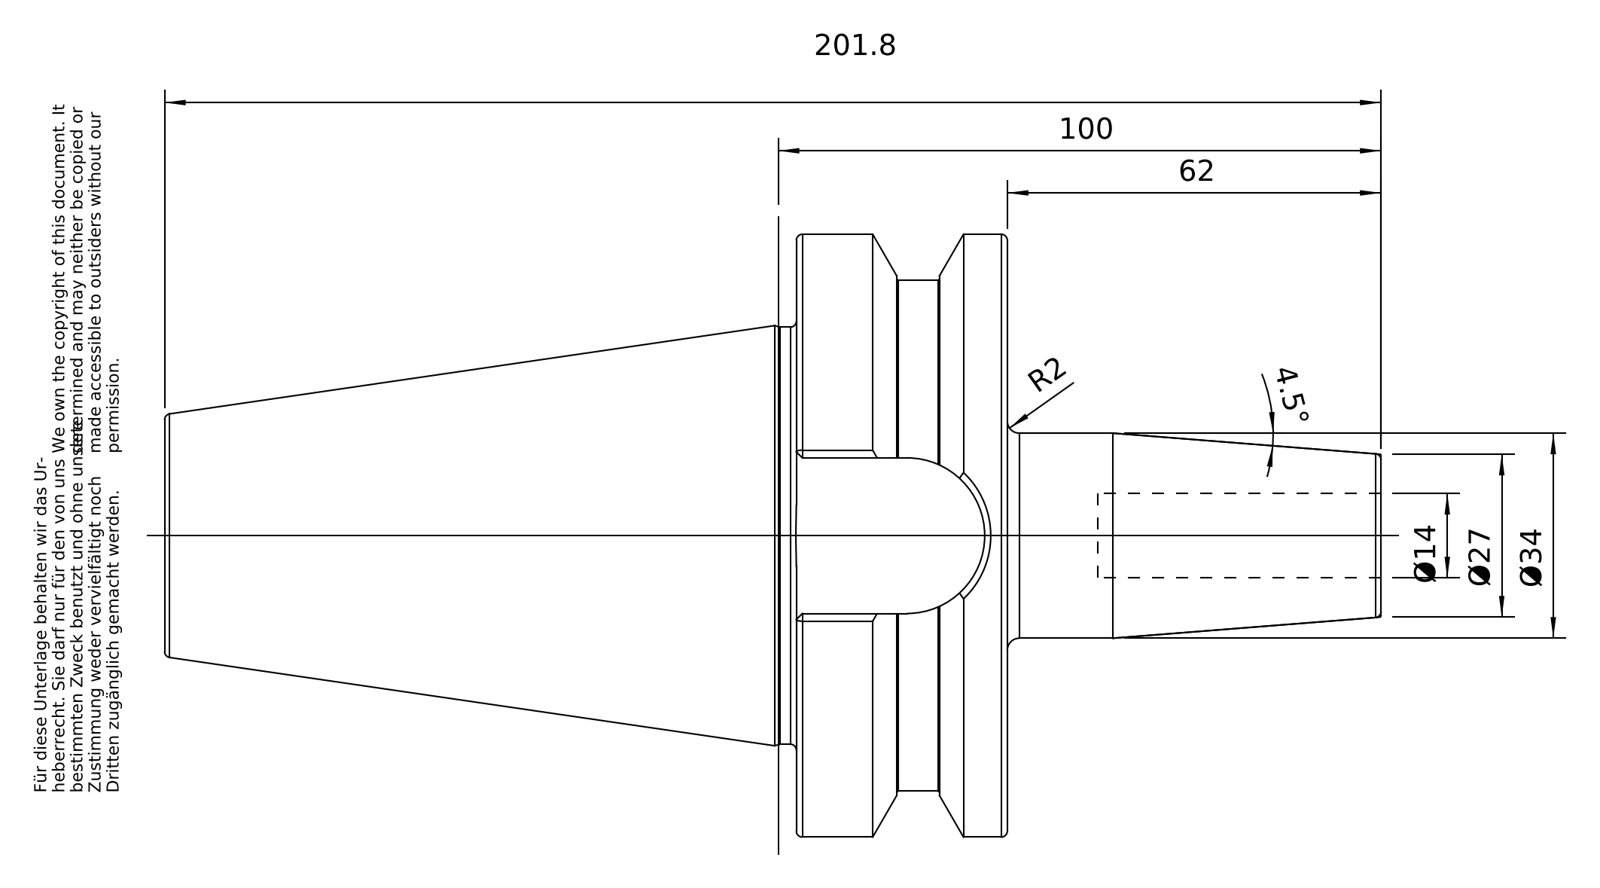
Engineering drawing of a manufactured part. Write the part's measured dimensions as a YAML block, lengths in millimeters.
part_name: "50-640-14"
step_written_by: "PRO/ENGINEER BY PARAMETRIC TECHNOLOGY CORPORATION, 2010430 (CONFIG_CONTROL_DESIGN)"
units: millimeters
bodies: {solids: 1, faces: 96, planar: 26, cylindrical: 22, other: 48}
overall_size: [201.8, 99.97, 99.97]
volume: 509439
surface_area: 59606
round_holes:
  - {diameter: 14, count: 1}
  - {diameter: 20.75, count: 1}
  - {diameter: 25.02, count: 1}
  - {diameter: 25.7, count: 1}
round_bosses_or_shafts:
  - {diameter: 99.97, count: 1}
  - {diameter: 84.75, count: 1}
  - {diameter: 69.15, count: 1}
  - {diameter: 34, count: 1}
  - {diameter: 24.01, count: 1}
partial_cylinders:
  - {radius: 12.9, count: 1}
face_to_face_distances: [35, 70.4, 104.8, 139.8, 25.8, 201.8, 97, 62, 154.8, 50]
